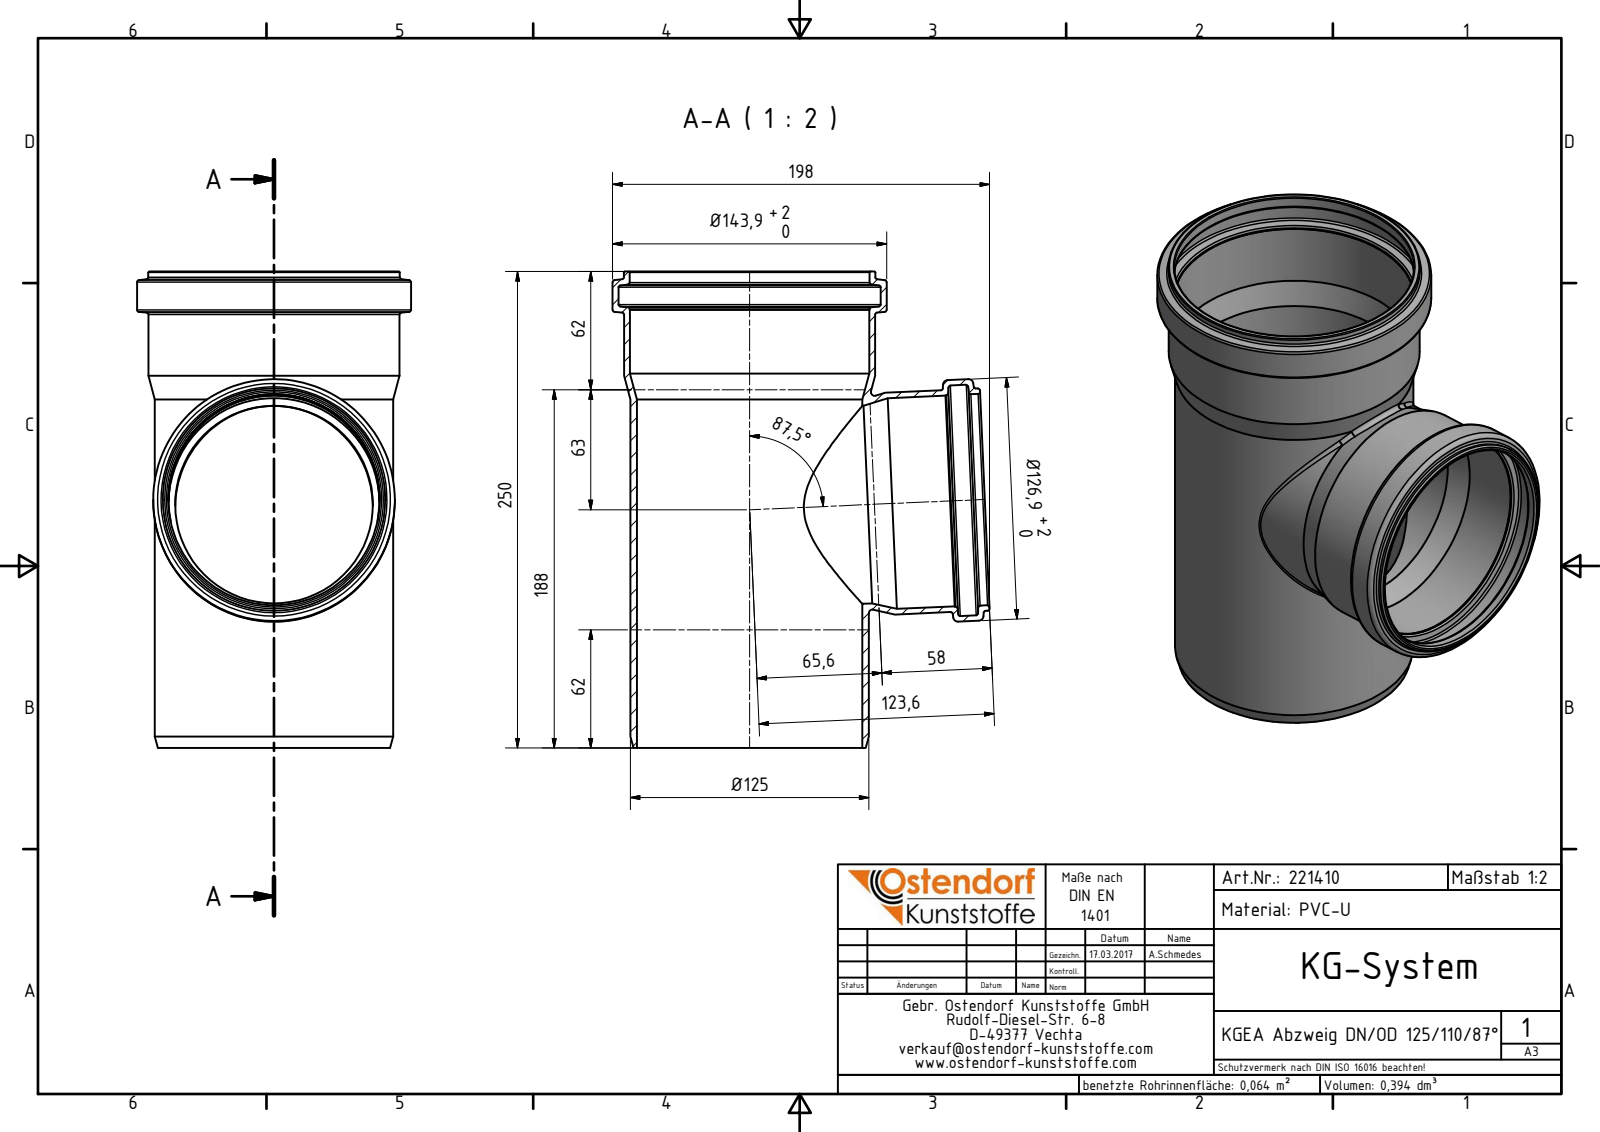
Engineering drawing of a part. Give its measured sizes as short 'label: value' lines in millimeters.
name: 221410 KGEA Abzweig DN_OD 125_110_87°
written by: Autodesk Inventor 2016 (AUTOMOTIVE_DESIGN)
unit: mm
bodies: 1 solid, 61 faces (5 planar, 19 cylindrical, 37 other)
size: 250 × 197.94 × 143.9
volume: 394 063 mm³; area: 245 957 mm²
holes: 1× ⌀103.8, 1× ⌀110.7, 1× ⌀111, 1× ⌀118.4, 1× ⌀121.1, 1× ⌀125.7, 1× ⌀125.9, 1× ⌀137.7
bosses: 1× ⌀143.9, 1× ⌀132.1, 1× ⌀131.9, 1× ⌀126.9, 1× ⌀125.2, 1× ⌀116.8, 1× ⌀116.5, 1× ⌀110.2
face distances: 250, 18.21, 229.83, 20.17
